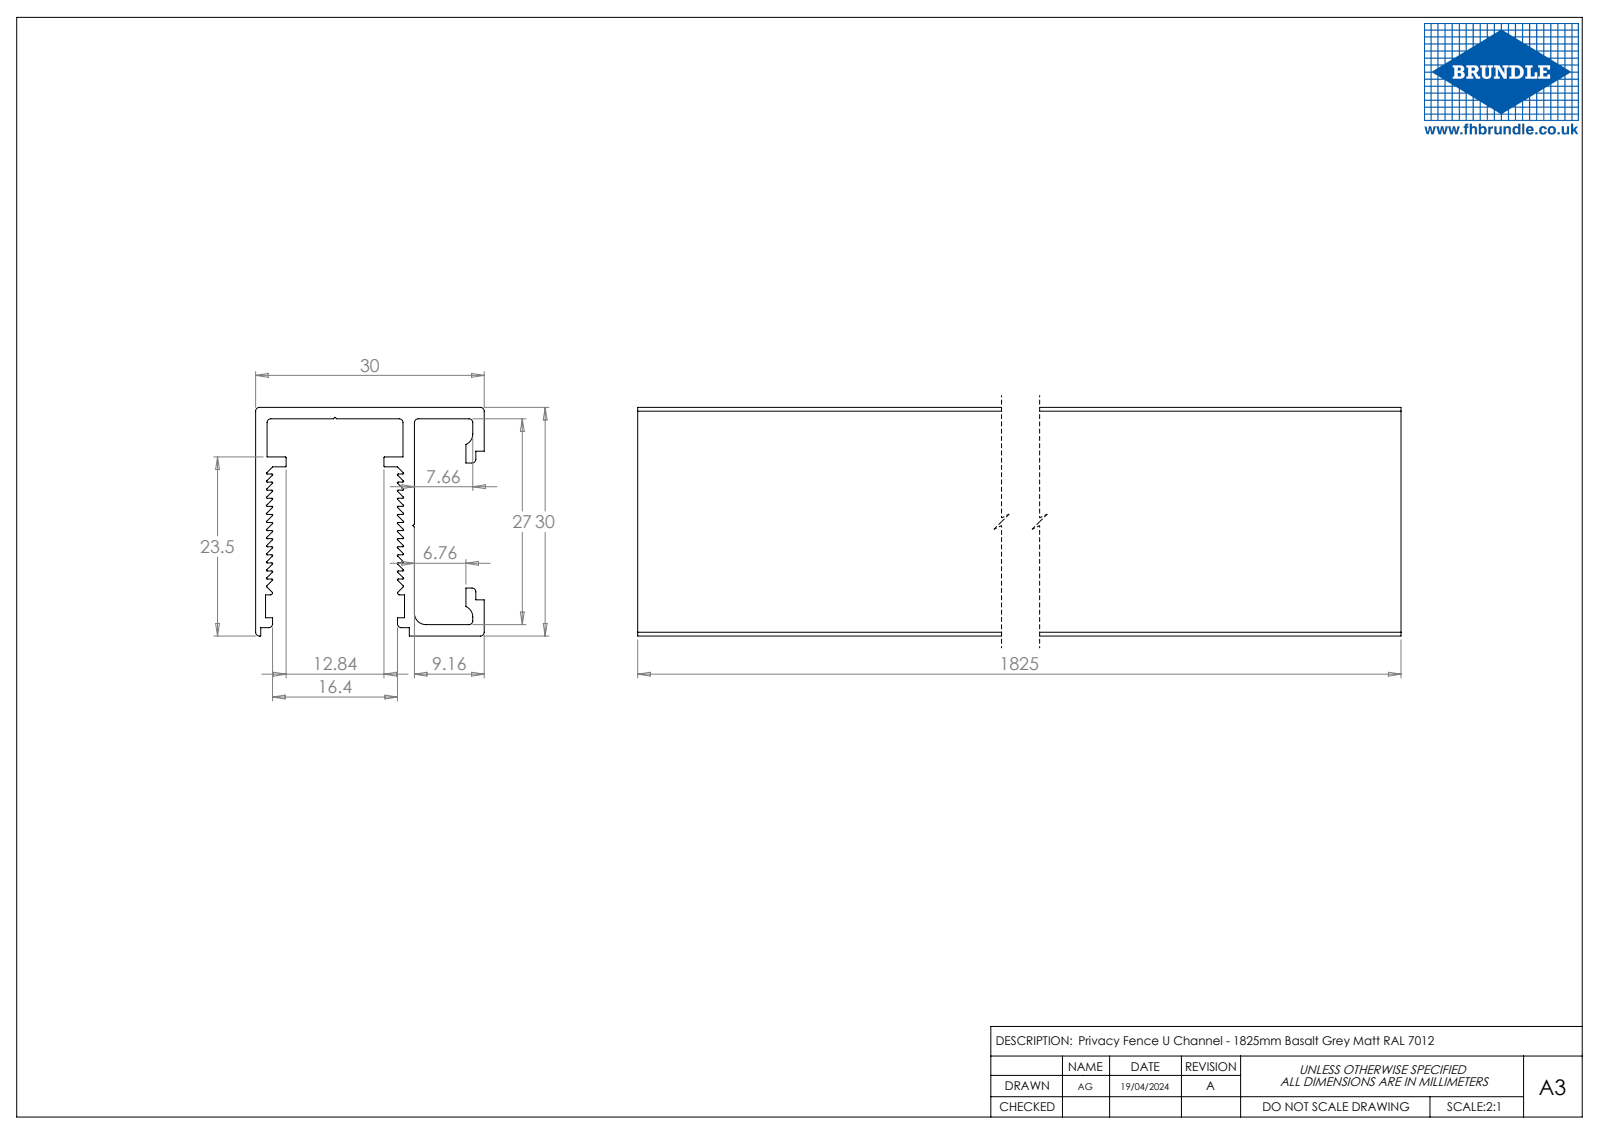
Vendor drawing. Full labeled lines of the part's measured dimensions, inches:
Part name (STEP PRODUCT): 76PFCK16A; 76PFCSA; 76PFUC16A; 76PFPTBS
STEP written by: SolidWorks 2023 (CONFIG_CONTROL_DESIGN)
Units: inches
Bodies: 3 solids, 281 faces (153 planar, 128 cylindrical, 0 other)
Overall size (bounding box): 71.969 × 1.181 × 1.181
Volume: 23.88 in³ · Surface area: 956.6 in²
Partial cylindrical surfaces — rounded edges, fillets, slot ends (radius × count): R0.02 ×23, R0.004 ×10, R0.059 ×6, R0.012 ×2
Main face-to-face distances: 0.059, 0.82, 0.03, 1.122, 1.179, 0.358, 0.089, 1.181, 0.118, 0.319
